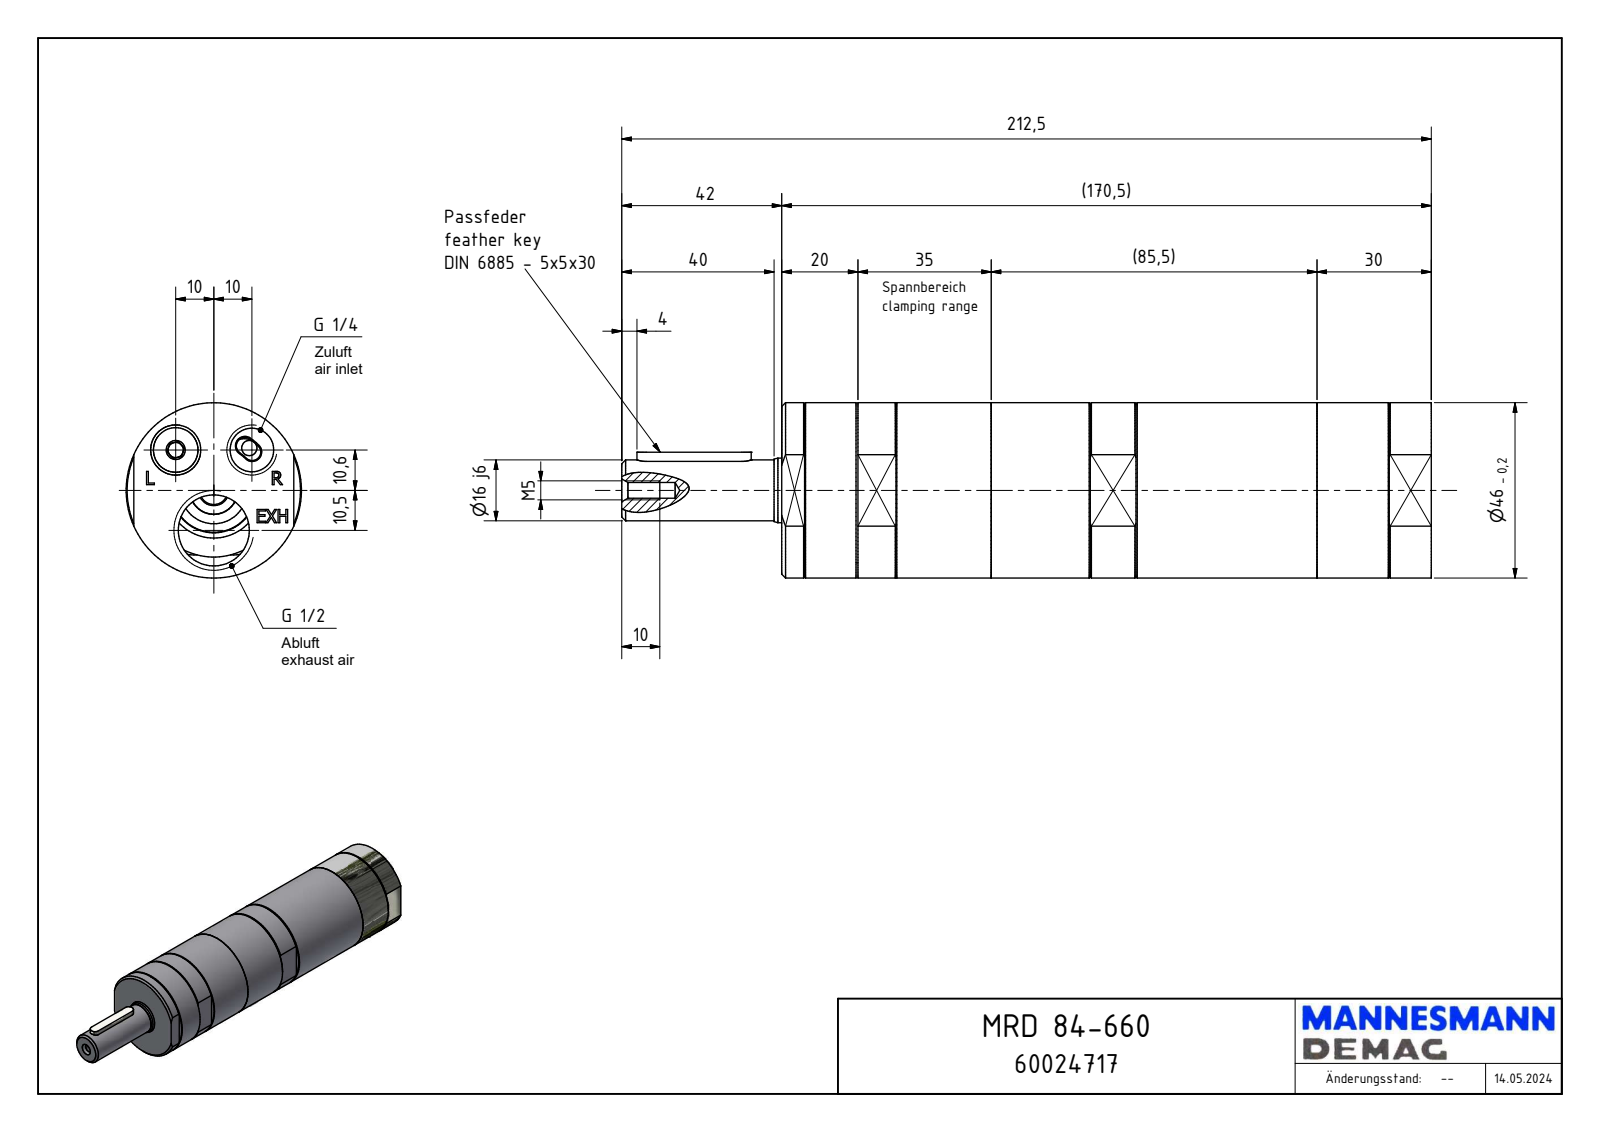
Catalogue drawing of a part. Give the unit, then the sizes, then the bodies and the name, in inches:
Units: inches
Overall size (bounding box): 8.366 × 1.811 × 1.811
Round holes (diameter × count): ⌀0.157 ×1, ⌀0.163 ×1, ⌀0.451 ×1, ⌀0.689 ×1, ⌀0.733 ×1, ⌀1.496 ×1, ⌀1.511 ×1
Round bosses / shafts (diameter × count): ⌀1.811 ×1, ⌀1.325 ×1, ⌀0.667 ×1, ⌀0.63 ×1
Partial cylindrical surfaces — rounded edges, fillets, slot ends (radius × count): R0.098 ×2, R0.197 ×2, R0.225 ×1
Main face-to-face distances: 6.713, 1.654, 0.787, 5.925, 0.768, 0.02, 5.945, 6.405, 5.637, 5.617
Hole centre spacings: 0.574, 0.919, 0.413, 0.787
Volume: 17.43 in³ · Surface area: 52.24 in²
Bodies: 1 solid, 177 faces (110 planar, 32 cylindrical, 35 other)
Part name (STEP PRODUCT): MRD 84-660_60024717
STEP written by: Autodesk Inventor 2018 (AUTOMOTIVE_DESIGN)
